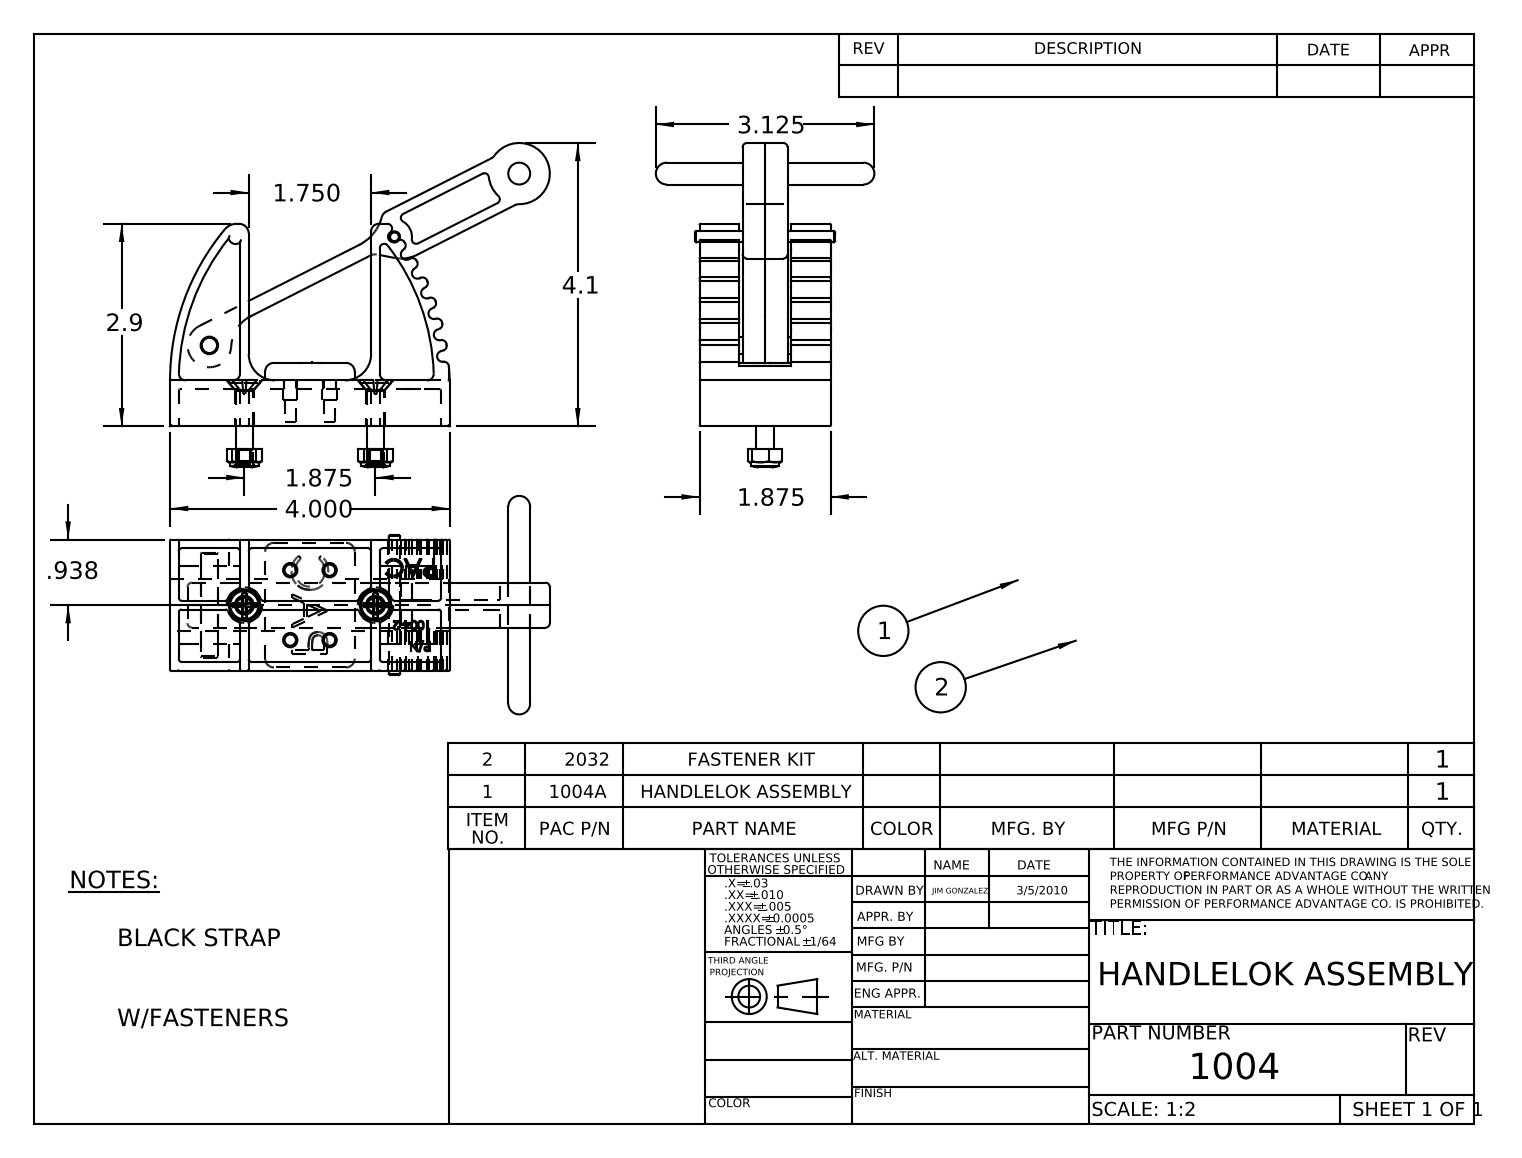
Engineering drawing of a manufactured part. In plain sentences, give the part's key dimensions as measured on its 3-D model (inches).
The part is named "1004 PIVOT PIN; 1004 PAD; 1004 STRAP (BLACK) - in use; 1004 (+1 more)". Its 3-D file was written by "SolidWorks 2014 (CONFIG_CONTROL_DESIGN)". It is 7 solids with 848 faces: 262 planar, 342 cylindrical and 244 other. Overall it measures 5.906 by 3.125 by 2.895 inches. Its volume is 6.799 cubic inches and its surface area 101.7 square inches. Round holes: 4 of diameter 0.17, 2 of diameter 0.266, 1 of diameter 0.156, 1 of diameter 0.156, 1 of diameter 0.25, 1 of diameter 0.313. Round bosses or shafts: 4 of diameter 0.205, 4 of diameter 0.187, 4 of diameter 0.162, 1 of diameter 0.625. Partial cylindrical surfaces (rounded edges, fillets, slot ends): 68 of radius 0.016, 32 of radius 0.041, 18 of radius 0.063, 12 of radius 0.125, 7 of radius 0.068, 7 of radius 0.07, 6 of radius 0.078, 4 of radius 0.094. The main face-to-face distances are 0.125, 0.375, 0.937, 0.563, 0.75, 1.875, 0.25, 1.75, 1, 1.5. The hole center spacings are 0.825, 1.317, 0.562, 1, 1.147, 1.875, 2, 3.148.
